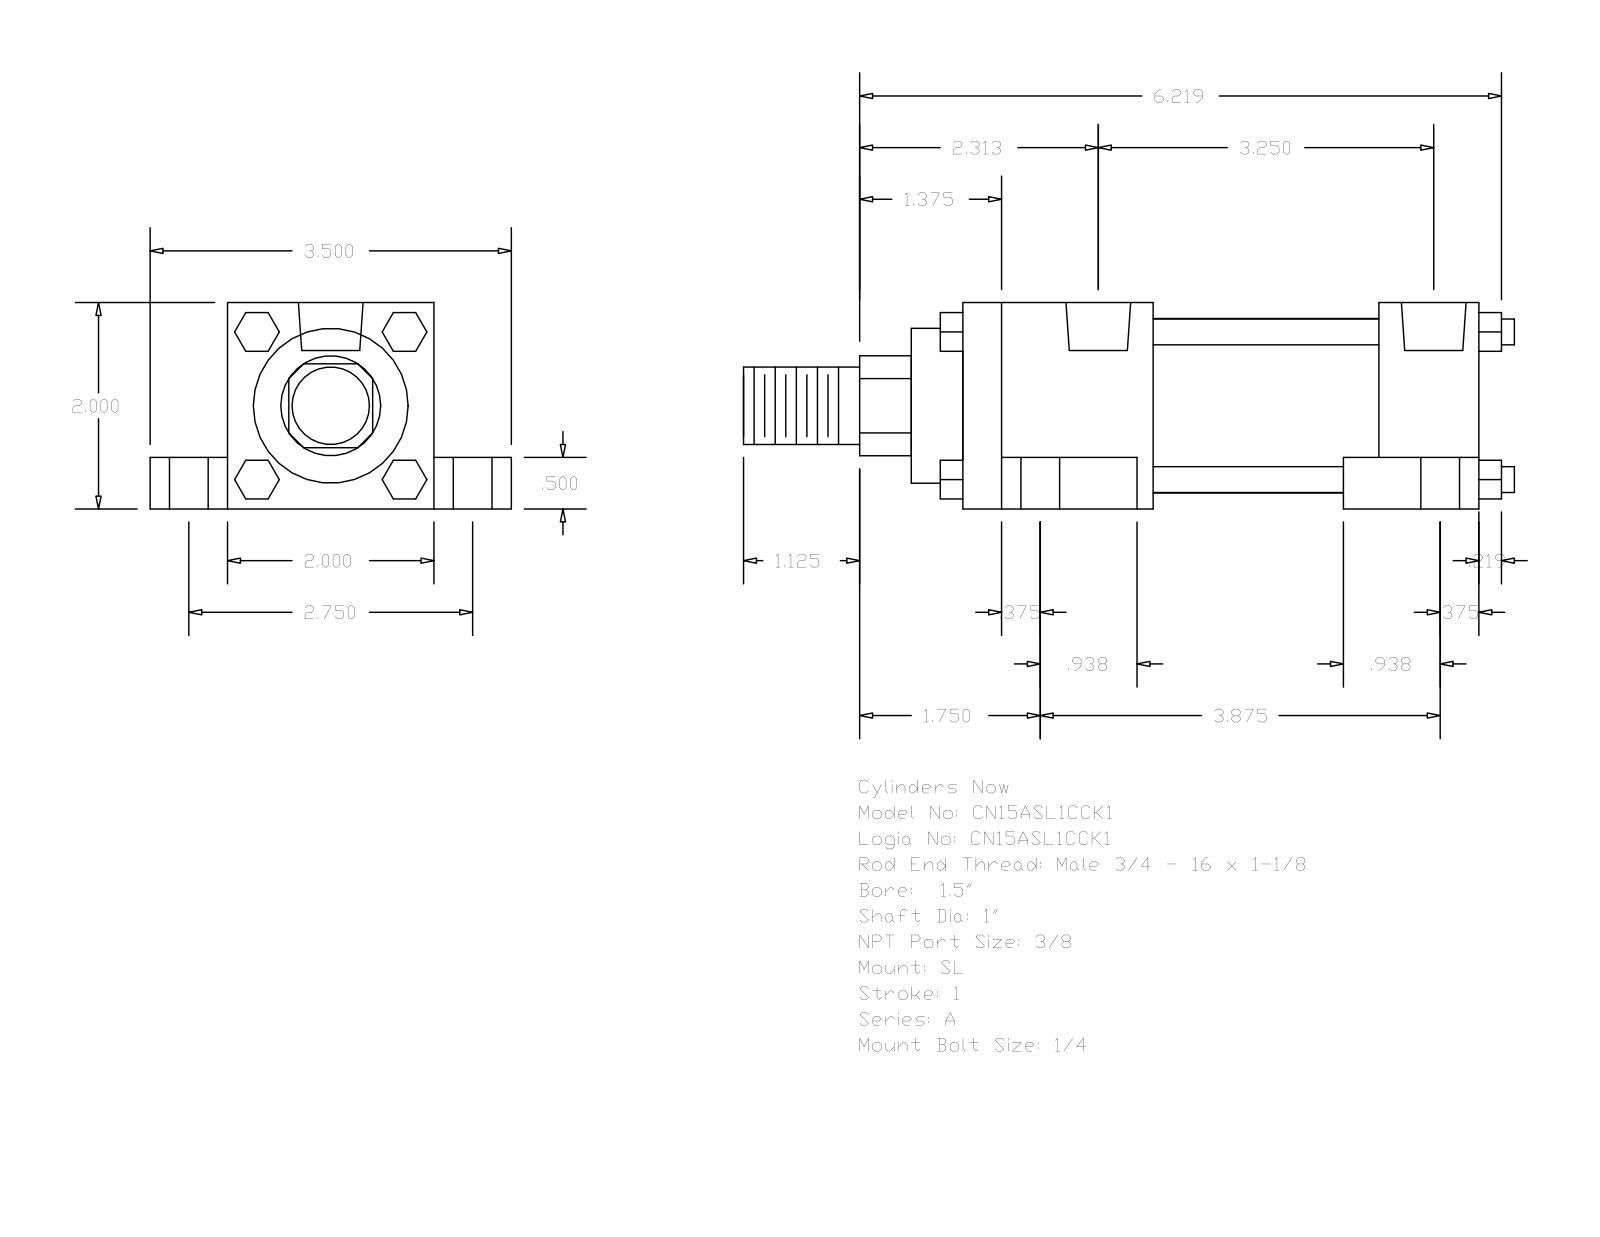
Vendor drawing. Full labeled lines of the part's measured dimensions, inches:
Part name (STEP PRODUCT): A_SL__0150_1
STEP written by: GSSL Pune (CONFIG_CONTROL_DESIGN)
Units: inches
Bodies: 0 solids, 148 faces (112 planar, 36 cylindrical, 0 other)
Overall size (bounding box): 7.469 × 3.5 × 2
Round holes (diameter × count): ⌀0.219 ×4, ⌀0.375 ×4, ⌀0.625 ×4, ⌀0.627 ×2
Round bosses / shafts (diameter × count): ⌀0.25 ×4, ⌀1.69 ×1, ⌀1.5 ×1, ⌀1 ×1, ⌀0.75 ×1
Partial cylindrical surfaces — rounded edges, fillets, slot ends (radius × count): R0.484 ×1
Main face-to-face distances: 2, 0.5, 1.5, 0.75, 2.75, 2.187, 1.844, 0.375, 5, 2.344
Hole centre spacings: 0.156, 1.376, 1.392, 1.485, 1.552, 2.75, 2.937, 3.094
